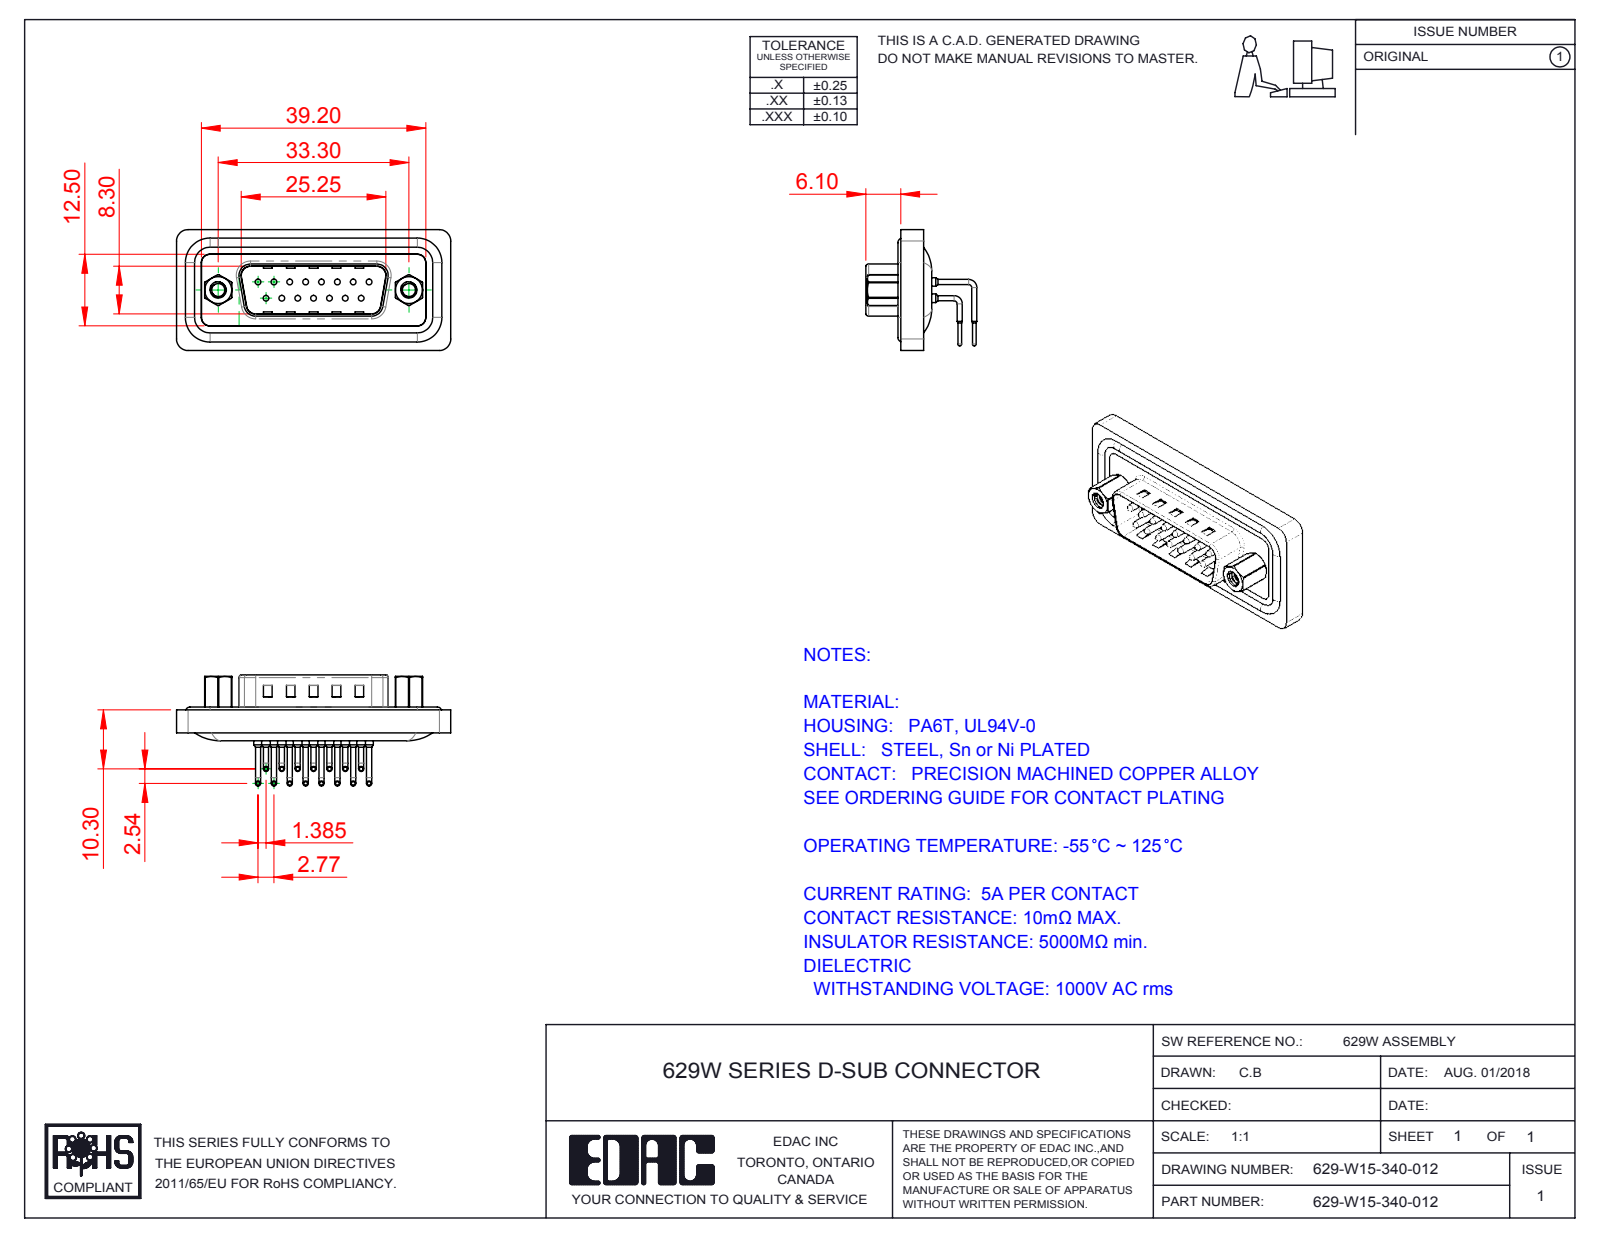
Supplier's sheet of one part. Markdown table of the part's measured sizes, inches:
| quantity | value |
| --- | --- |
| part name | 629W Contact Row 2; 629W 4-40 Hex Standoff; 629-W15-340-012; 629W 4-40 Threaded Rivet_Stabilizer (+4 more) |
| STEP written by | SolidWorks 2016 (CONFIG_CONTROL_DESIGN) |
| units | inches |
| bodies | 23 solids, 2156 faces (1133 planar, 778 cylindrical, 245 other) |
| overall size | 1.885 × 0.831 × 0.763 |
| volume | 0.301 in³ |
| surface area | 13.15 in² |
| round holes (diameter × count) | 0.039 × 15, 0.059 × 15, 0.067 × 15, 0.079 × 15, 0.089 × 2, 0.09 × 2, 0.157 × 2, 0.189 × 2, 0.197 × 2 |
| round bosses / shafts (diameter × count) | 0.035 × 30, 0.059 × 15, 0.026 × 15, 0.063 × 4, 0.193 × 2, 0.11 × 2, 0.197 × 1 |
| partial cylindrical surfaces (radius × count) | 0.079 × 16, 0.04 × 15, 0.059 × 14, 0.02 × 8, 0.106 × 6, 0.035 × 4, 0.063 × 4, 0.169 × 4 |
| main face-to-face distances | 0.016, 0.063, 0.043, 0.098, 0.114, 0.02, 0.161, 0.177, 0.222, 0.608 |
| hole center spacings | 0.124, 0.109, 0.218, 0.327, 0.125, 0.124, 0.436, 0.198 |
